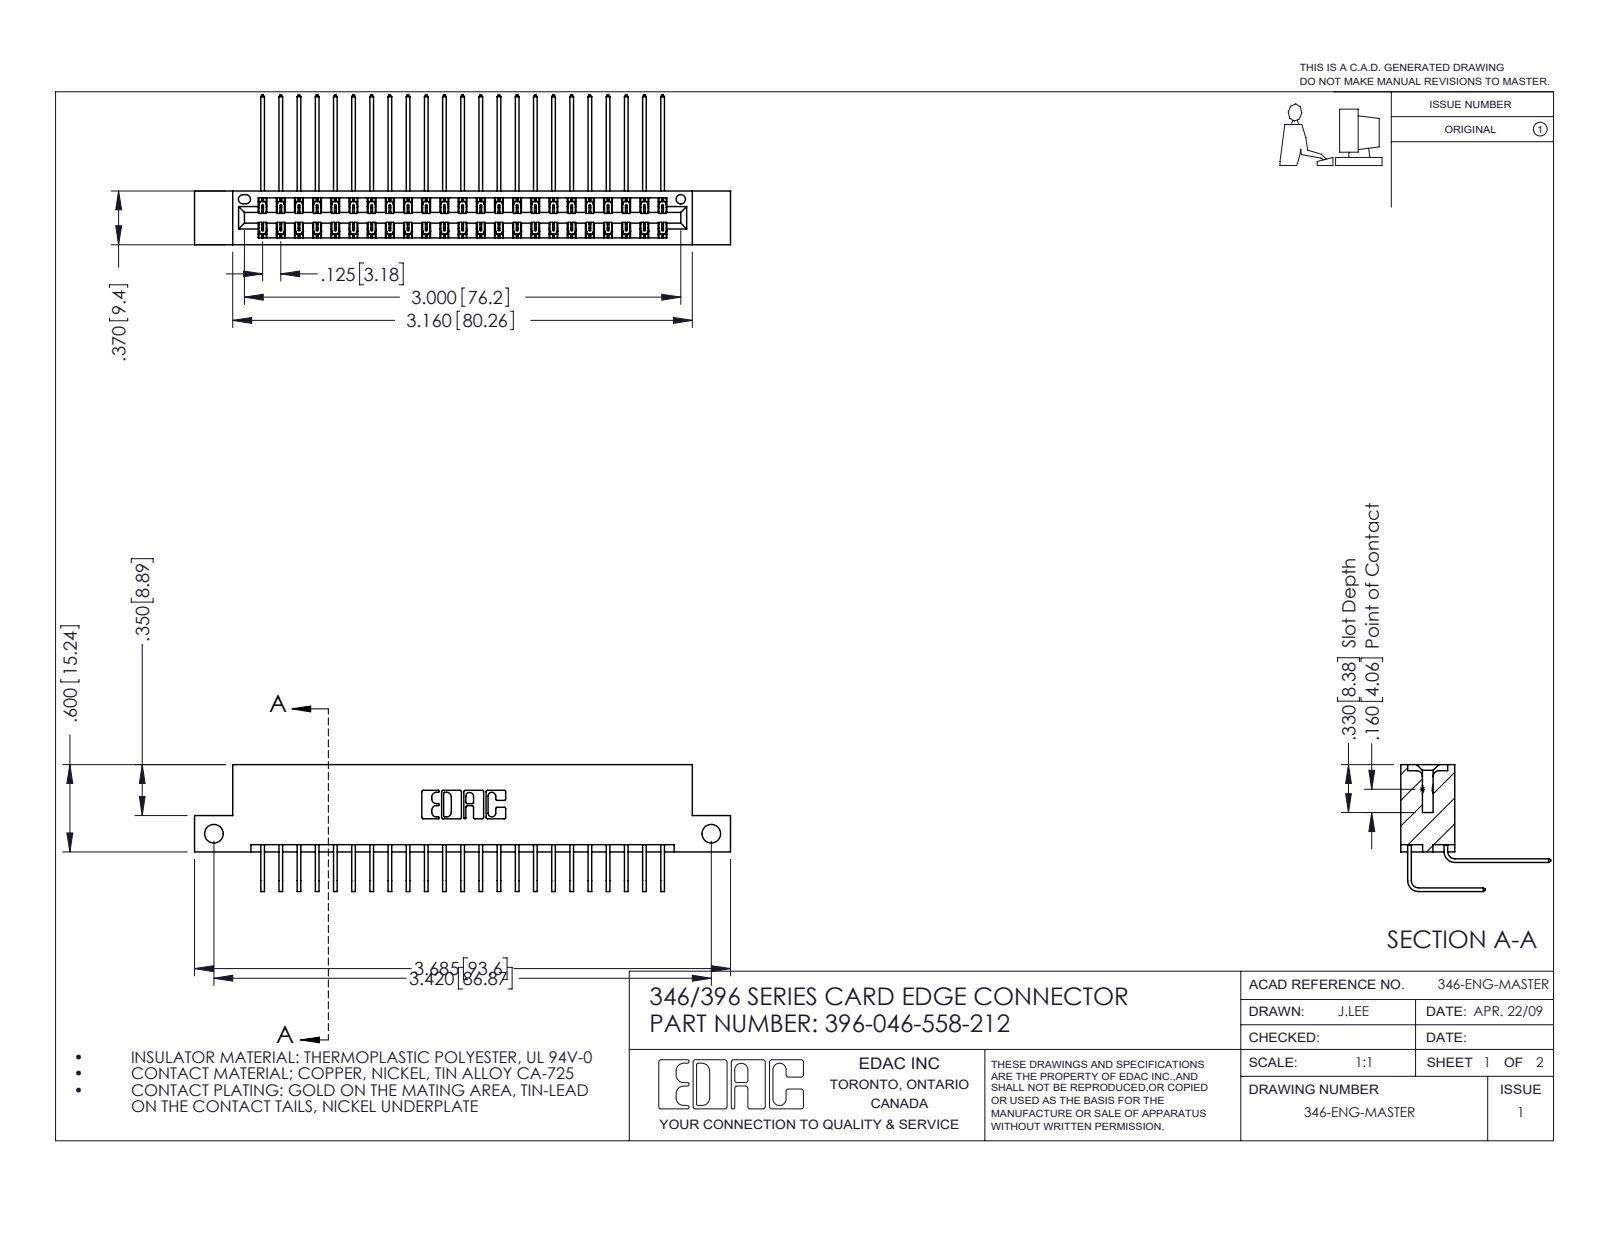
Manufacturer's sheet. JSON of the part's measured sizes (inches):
{"part_name": "345-292-001_558 559 Tail - 1; 346 Part_Flush Mounting Lugs - Side Mount; 396-046-558-212; 345-292-001_558 Tail - 2", "step_written_by": "SolidWorks 2016 (CONFIG_CONTROL_DESIGN)", "units": "inches", "bodies": {"solids": 47, "faces": 2606, "planar": 1778, "cylindrical": 828, "other": 0}, "overall_size": [3.685, 1.03, 0.873], "volume_in3": 0.559, "surface_area_in2": 20.81, "round_holes": [[0.128, 2], [0.064, 1]], "partial_cylinders_radius": [[0.006, 69], [0.01, 22], [0.007, 6], [0.031, 6], [0.026, 3], [0.014, 2], [0.022, 2], [0.024, 2]], "face_to_face_distances": [0.322, 0.048, 0.25, 0.025, 0.37, 0.298, 0.072, 0.275, 0.148, 0.222], "hole_center_spacings": [3.42]}
